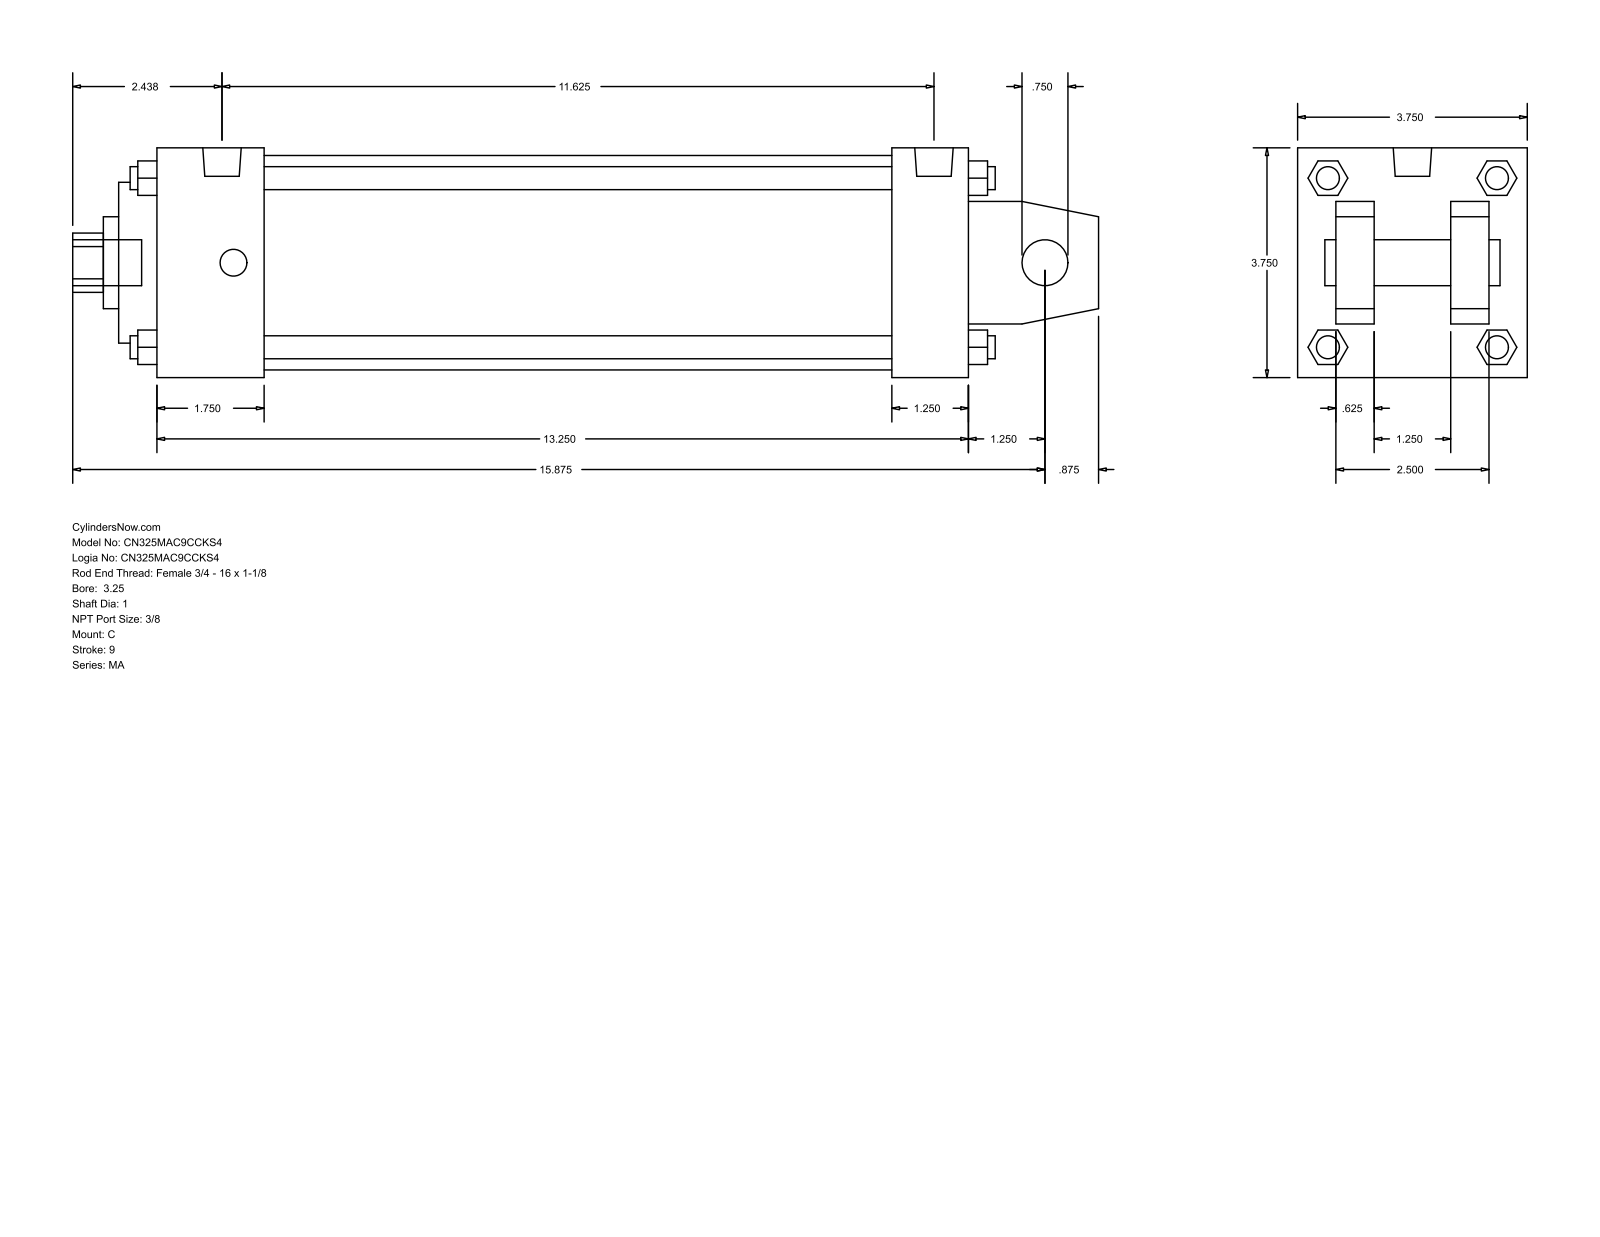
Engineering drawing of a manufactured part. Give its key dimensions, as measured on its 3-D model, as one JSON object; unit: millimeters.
{"part_name": "MA_C__0325_1", "step_written_by": "GSSL Pune (CONFIG_CONTROL_DESIGN)", "units": "millimeters", "bodies": {"solids": 0, "faces": 141, "planar": 109, "cylindrical": 32, "other": 0}, "overall_size": [425.45, 95.25, 95.25], "round_holes": [[19.05, 1], [25.4, 1], [38.1, 1], [66.67, 1], [88.9, 1]], "round_bosses_or_shafts": [[11.11, 4], [9.53, 4], [15.93, 2], [19.05, 1]], "partial_cylinders_radius": [[12.29, 1]], "face_to_face_distances": [95.24, 15.87, 63.5, 336.56, 31.74, 79.37, 47.63, 304.81, 31.75, 44.46]}
